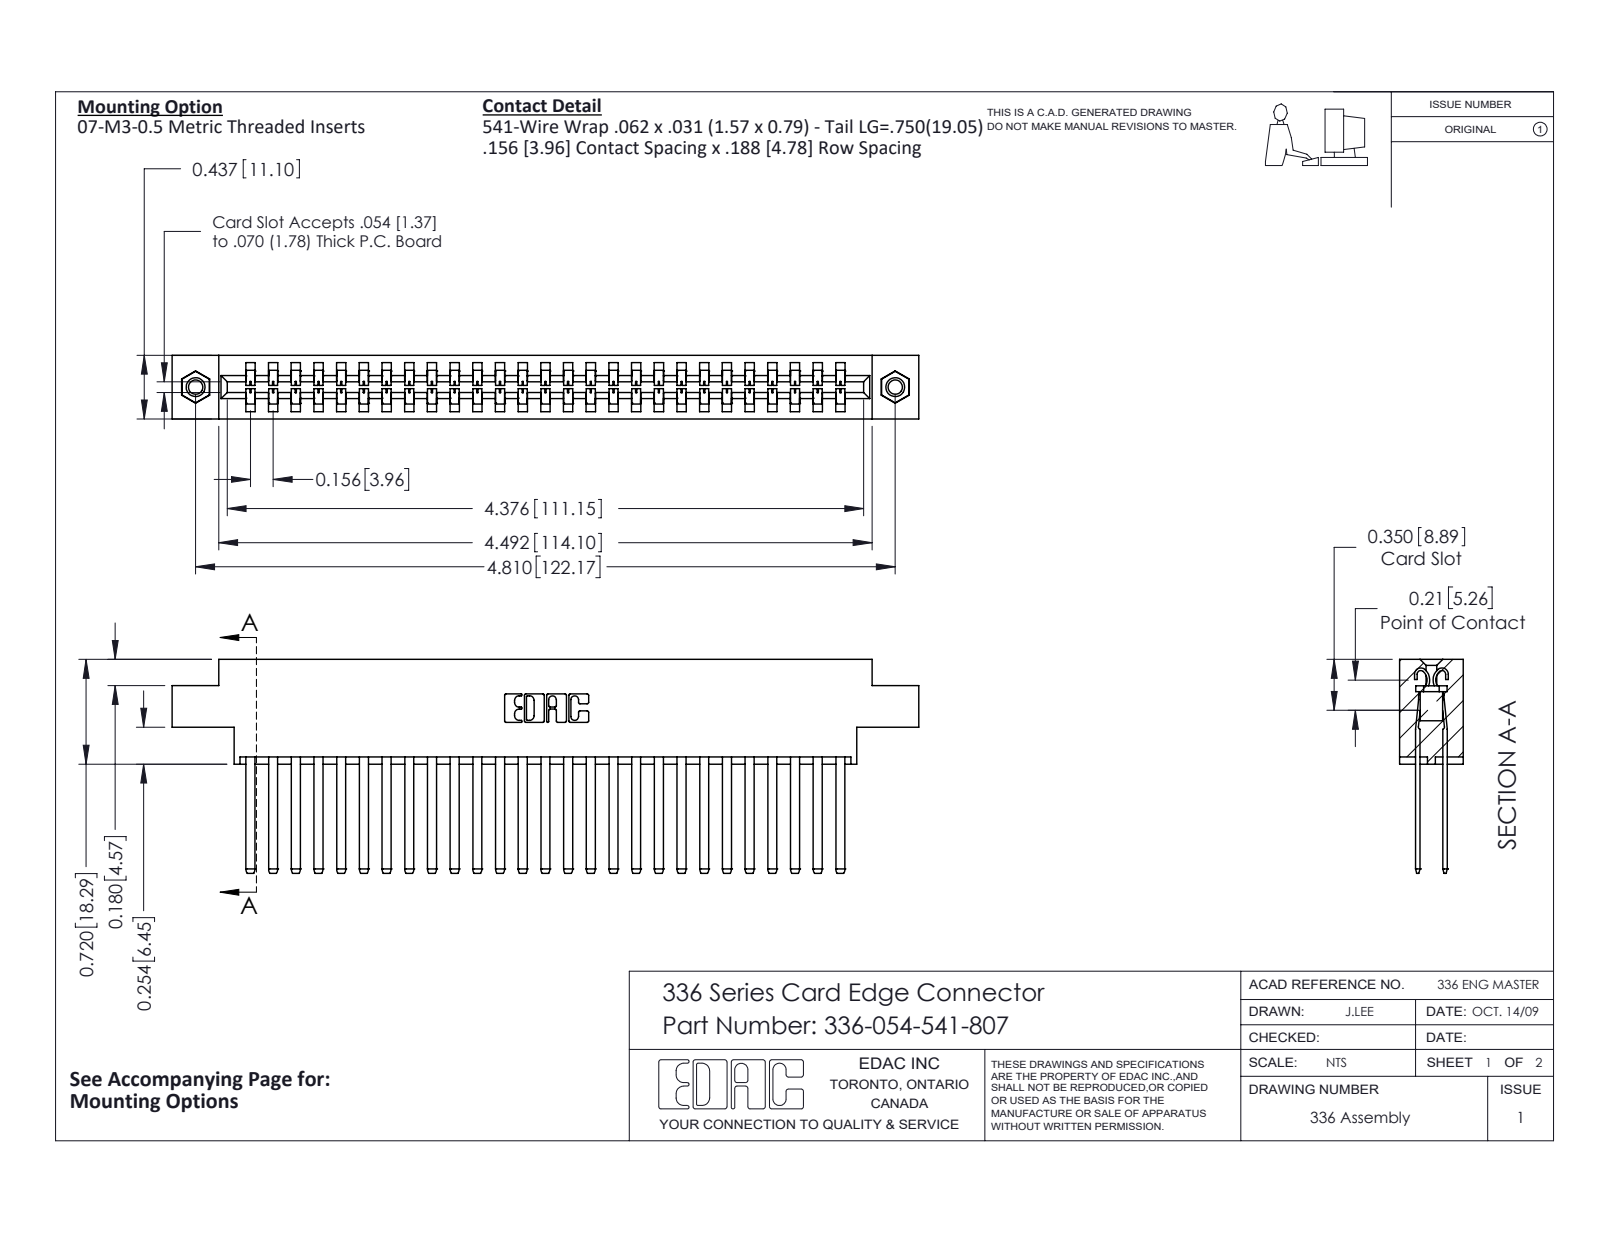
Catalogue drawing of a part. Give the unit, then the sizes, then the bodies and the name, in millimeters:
Units: millimetres
Overall size (bounding box): 130.4 × 37.3 × 11.1
Round holes (diameter × count): ⌀2.5 ×2, ⌀3.2 ×2, ⌀4 ×2
Round bosses / shafts (diameter × count): ⌀3.9 ×2
Partial cylindrical surfaces — rounded edges, fillets, slot ends (radius × count): R0.1 ×108, R1.4 ×54, R0.3 ×22, R0.2 ×6, R0.8 ×6, R0.6 ×4, R1 ×4, R0.7 ×3
Main face-to-face distances: 4.8, 8.3, 3.6, 7.5, 2.8, 0.8, 11.1, 0.8, 4.6, 3.7
Hole centre spacings: 122.2
Volume: 19 650 mm³ · Surface area: 24 950 mm²
Bodies: 57 solids, 2446 faces (1510 planar, 920 cylindrical, 16 other)
Part name (STEP PRODUCT): 336-054-541-807; 336 Part_Offset - .156 Dia - TI; 336-290-001_336-290-541; 345-250-001_345-250-005-103
STEP written by: SolidWorks 2020 (CONFIG_CONTROL_DESIGN)
